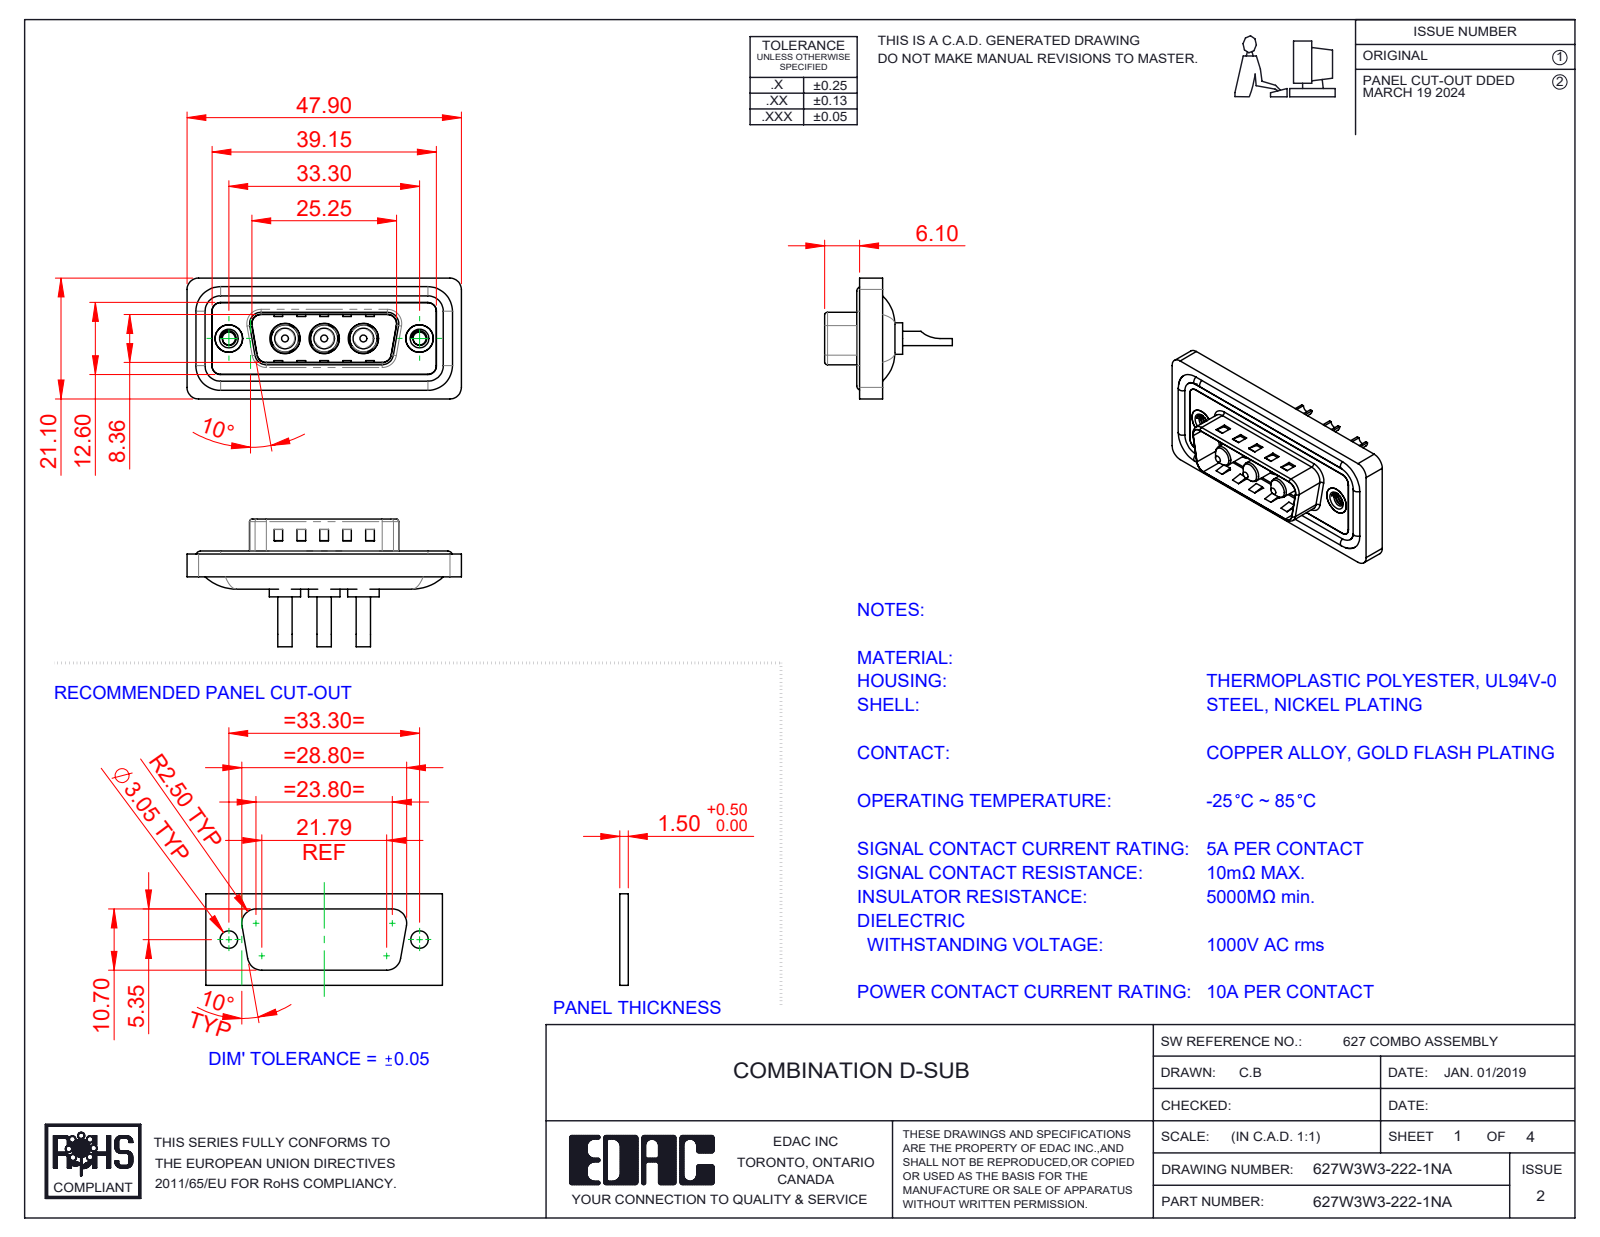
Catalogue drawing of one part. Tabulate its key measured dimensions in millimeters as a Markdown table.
| quantity | value |
| --- | --- |
| part name | 627Combo Waterproof Housing_15 Contacts; 627Combo Shell Front_15 Contacts; 627Combo Threaded Rivet_A; Power Pin_10A SC (+3 more) |
| STEP written by | SolidWorks 2023 (CONFIG_CONTROL_DESIGN) |
| units | millimeters |
| bodies | 13 solids, 580 faces (213 planar, 252 cylindrical, 115 other) |
| overall size | 47.9 × 22.3 × 21.1 |
| volume | 5 579 mm³ |
| surface area | 8 894 mm² |
| round holes (diameter × count) | 1.7 × 3, 4.85 × 3, 5.3 × 3, 2.26 × 2, 4 × 2, 4.8 × 2, 5 × 2 |
| round bosses / shafts (diameter × count) | 1.6 × 4, 5.5 × 3, 5.2 × 3, 4.75 × 3, 3.75 × 3, 3.6 × 3, 2.5 × 3, 4.9 × 2 |
| partial cylindrical surfaces (radius × count) | 1.5 × 26, 2 × 20, 0.5 × 8, 1.6 × 8, 0.25 × 4, 0.6 × 4, 0.65 × 4, 0.9 × 4 |
| main face-to-face distances | 0.4, 1.1, 1.5, 0.5, 1.6, 3.1, 2.9, 4, 0.82, 9.58 |
| hole center spacings | 6.85, 9.8, 16.65, 23.5, 13.7, 33.3 |
